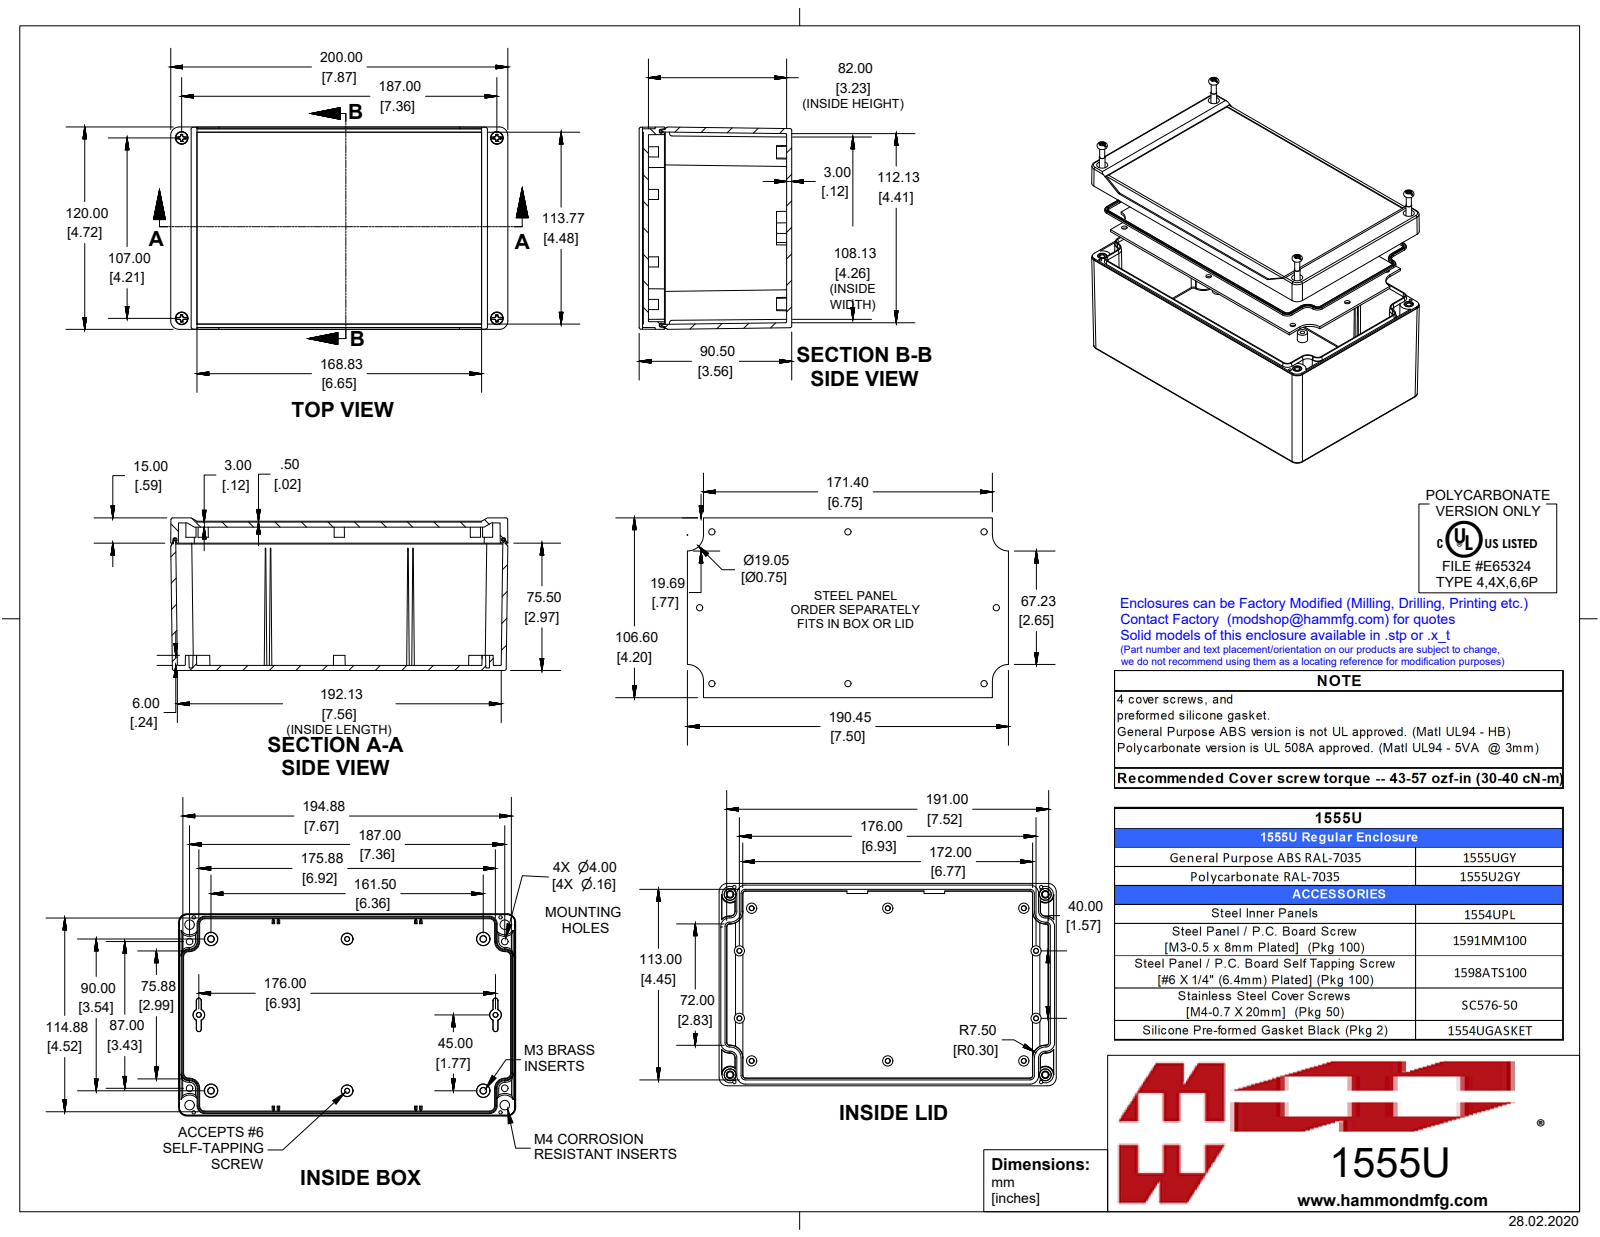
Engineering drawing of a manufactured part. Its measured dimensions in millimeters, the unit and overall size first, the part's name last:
Units: millimetres
Overall size (bounding box): 200 × 120 × 90.5
Round holes (diameter × count): ⌀2 ×4, ⌀2.5 ×4, ⌀3.3 ×4, ⌀3.5 ×4, ⌀7 ×4
Round bosses / shafts (diameter × count): ⌀6.4 ×4, ⌀6 ×4, ⌀5.5 ×4, ⌀5.3 ×4, ⌀4.8 ×4, ⌀3.9 ×4, ⌀3.9 ×4, ⌀3.8 ×4
Partial cylindrical surfaces — rounded edges, fillets, slot ends (radius × count): R0.5 ×40, R1 ×8, R5 ×8, R4.7 ×4, R1.5 ×2
Main face-to-face distances: 3, 85, 88, 82, 1.5, 9.5, 12.5, 11, 3.5, 4.5
Hole centre spacings: 5, 15.3, 16.4, 99.3, 103.4, 111.4, 172.2, 174.5
Volume: 331 800 mm³ · Surface area: 238 500 mm²
Bodies: 15 solids, 1386 faces (416 planar, 328 cylindrical, 642 other)
Part name (STEP PRODUCT): 1555U2GY
STEP written by: SolidWorks 2019 (AUTOMOTIVE_DESIGN)
